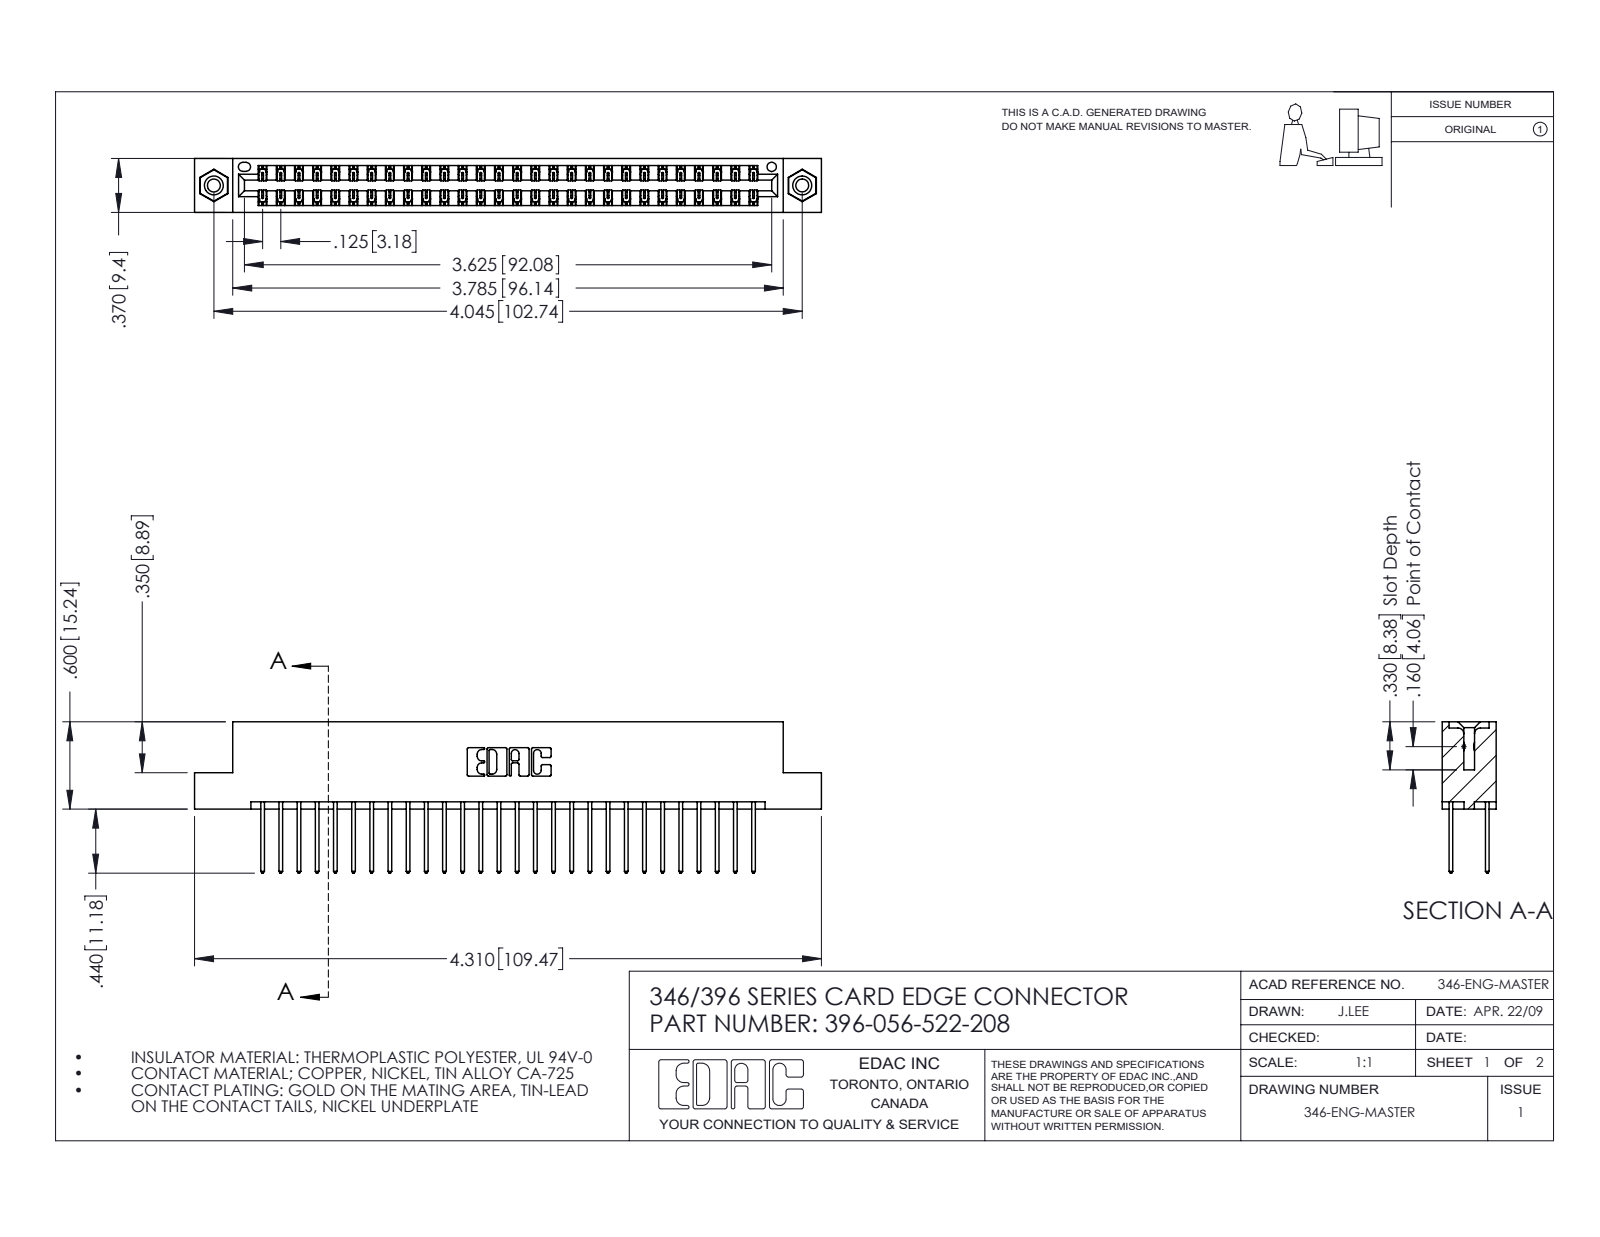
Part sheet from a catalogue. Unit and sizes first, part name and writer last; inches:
Units: inches
Overall size (bounding box): 4.31 × 1.04 × 0.37
Round holes (diameter × count): ⌀0.089 ×2, ⌀0.125 ×2, ⌀0.156 ×2, ⌀0.064 ×1
Round bosses / shafts (diameter × count): ⌀0.155 ×2
Partial cylindrical surfaces — rounded edges, fillets, slot ends (radius × count): R0.006 ×84, R0.01 ×56, R0.01 ×22, R0.007 ×6, R0.031 ×6, R0.026 ×3, R0.014 ×2, R0.022 ×2
Main face-to-face distances: 0.048, 0.322, 0.25, 0.37, 0.072, 0.298, 0.025, 0.275, 0.148, 0.222
Hole centre spacings: 0.246, 3.837, 4.045
Volume: 0.653 in³ · Surface area: 23.53 in²
Bodies: 59 solids, 3094 faces (2068 planar, 1010 cylindrical, 16 other)
Part name (STEP PRODUCT): 345-292-001_345-293-122; 396-056-522-208; 345-250-001_345-250-003-102; 346 Part_Flush Mounting Lugs - 0.156 Dia-TI
STEP written by: SolidWorks 2016 (CONFIG_CONTROL_DESIGN)
